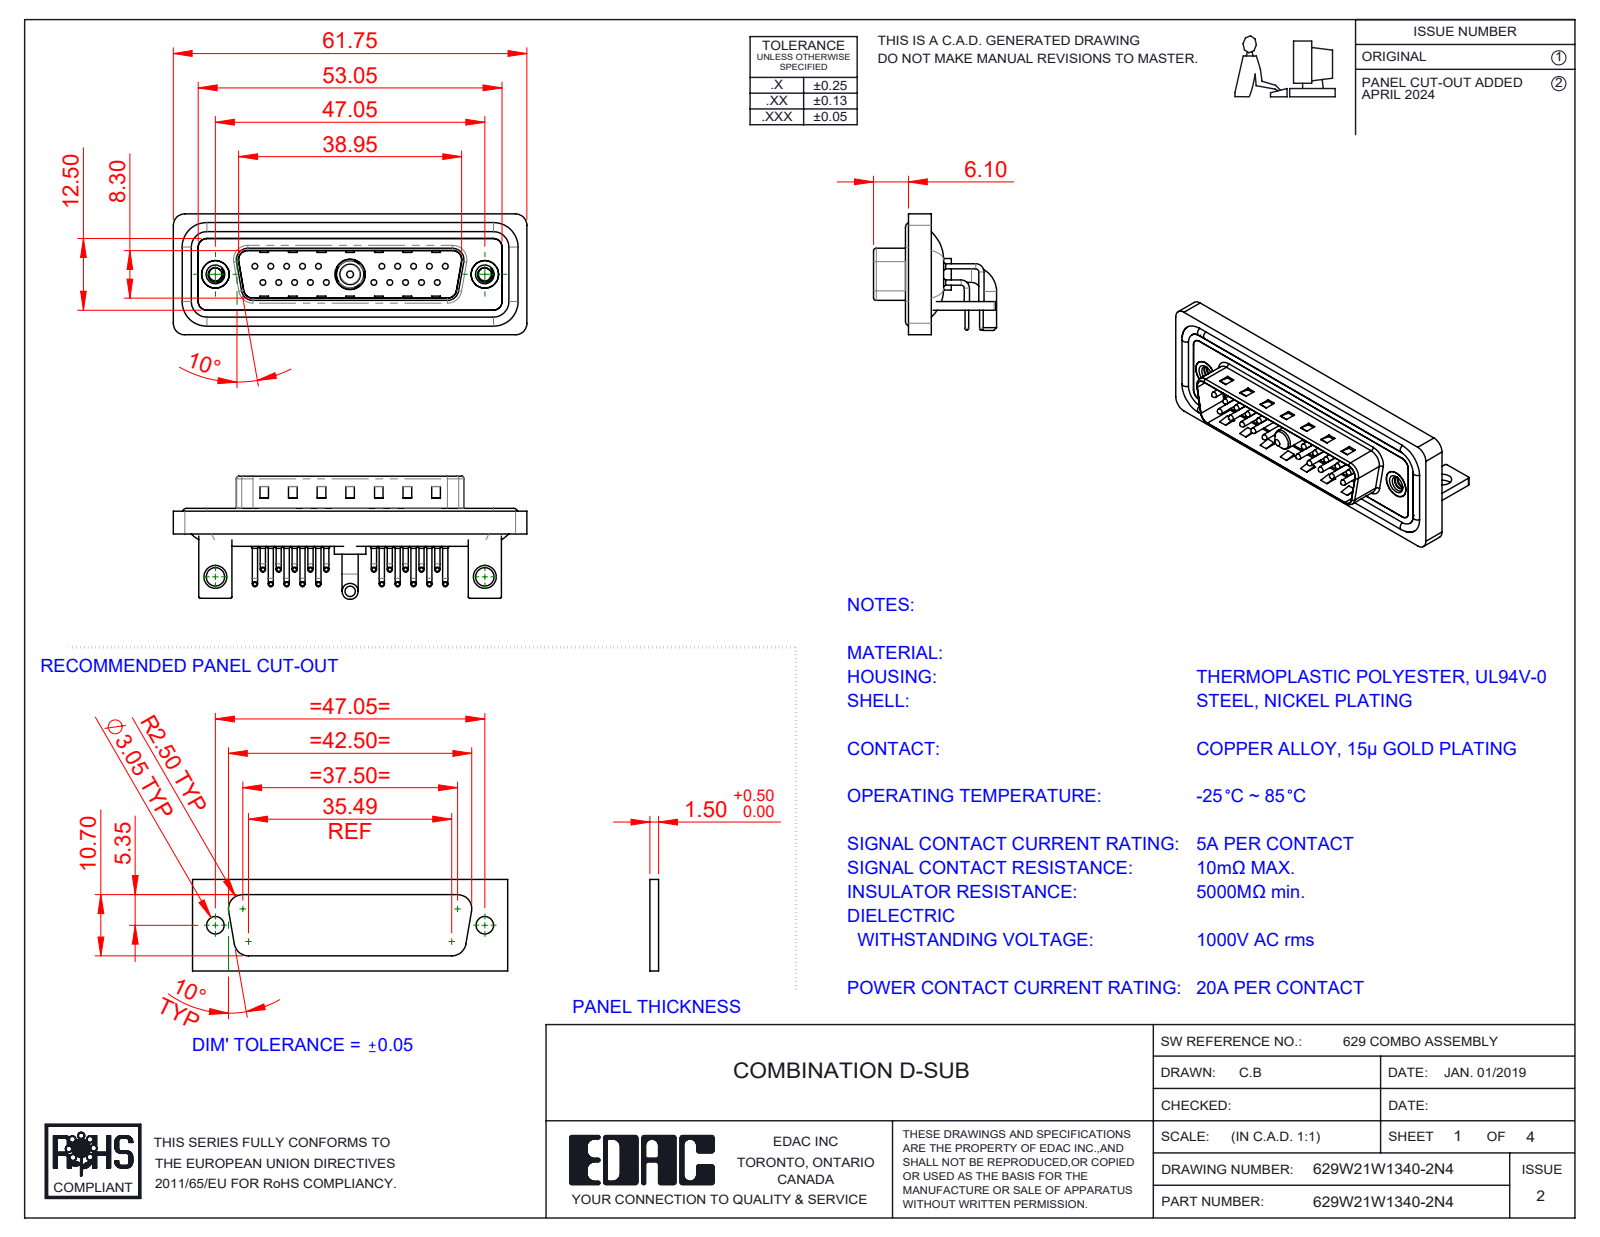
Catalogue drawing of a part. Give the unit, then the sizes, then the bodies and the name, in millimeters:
Units: millimetres
Overall size (bounding box): 61.75 × 21.5 × 21.1
Round holes (diameter × count): ⌀0.75 ×20, ⌀1.6 ×20, ⌀2 ×20, ⌀2.26 ×2, ⌀3.2 ×2, ⌀4 ×2, ⌀4.8 ×2, ⌀5 ×2, ⌀4.85 ×1, ⌀5.3 ×1
Round bosses / shafts (diameter × count): ⌀0.9 ×40, ⌀1.5 ×20, ⌀1 ×20, ⌀0.65 ×20, ⌀1.6 ×4, ⌀4.9 ×2, ⌀2.8 ×2, ⌀5.5 ×1
Partial cylindrical surfaces — rounded edges, fillets, slot ends (radius × count): R1.01 ×20, R2 ×19, R1.5 ×18, R0.25 ×16, R0.5 ×9, R1.6 ×8, R0.6 ×4, R0.65 ×4
Main face-to-face distances: 0.4, 0.8, 2.1, 2.9, 1.5, 1.1, 4.1, 1.6, 4.5, 3.7
Hole centre spacings: 3.16, 2.77, 5.54, 8.31, 5.04, 19.39, 20.97, 22.16
Volume: 7 695 mm³ · Surface area: 13 308 mm²
Bodies: 31 solids, 2766 faces (1519 planar, 947 cylindrical, 300 other)
Part name (STEP PRODUCT): 629Combo Waterproof Housing_25 Contacts; 629W21W1340-2N4; 629Combo Contact Row 1; 629Combo Shell Rear_25 Contacts (+6 more)
STEP written by: SolidWorks 2023 (CONFIG_CONTROL_DESIGN)
